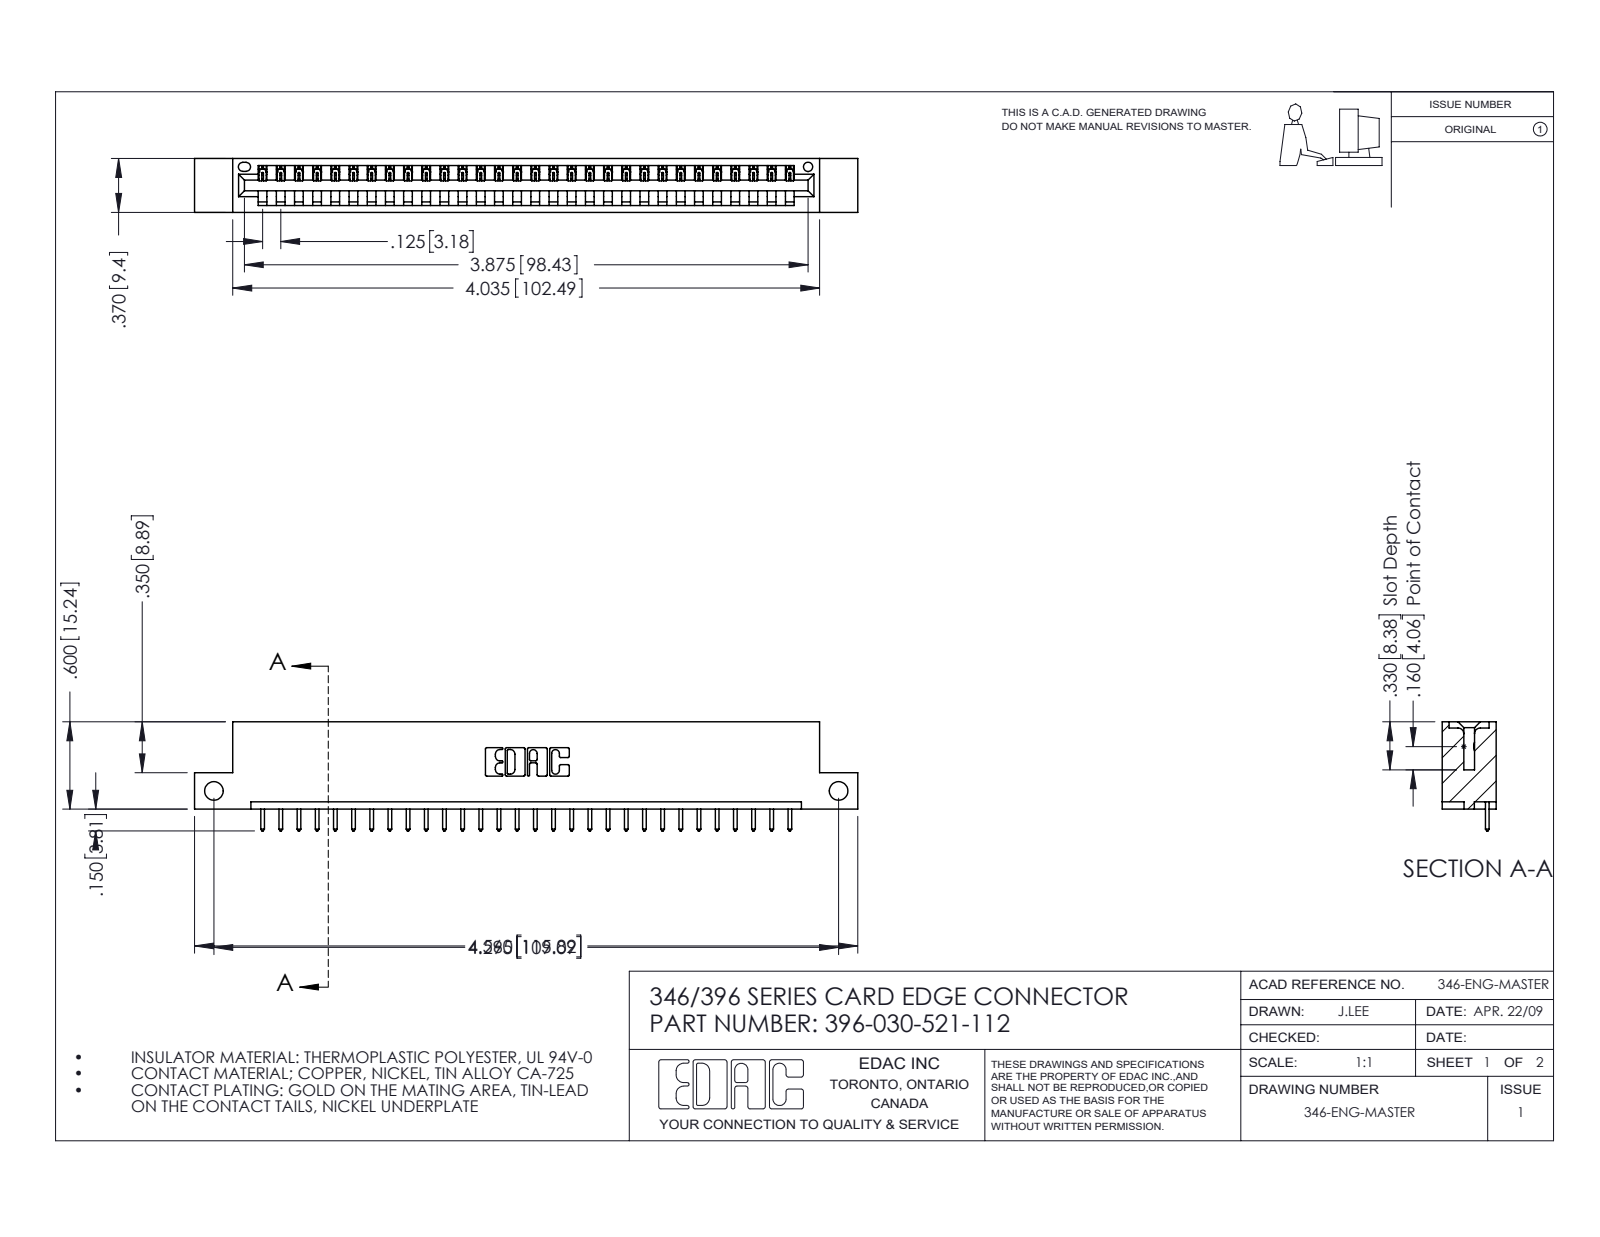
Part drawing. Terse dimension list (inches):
name: 345-292-001_345-293-121; 396-030-521-112; 346 Part_Flush Mounting Lugs - Side Mount
written by: SolidWorks 2016 (CONFIG_CONTROL_DESIGN)
unit: in
bodies: 31 solids, 1862 faces (1276 planar, 586 cylindrical, 0 other)
size: 4.56 × 0.75 × 0.37
volume: 0.661 in³; area: 20.03 in²
holes: 2× ⌀0.128, 1× ⌀0.064
rounds: 60× R0.006, 60× R0.01, 22× R0.01, 6× R0.007, 6× R0.031, 3× R0.026, 2× R0.031, 2× R0.04
face distances: 0.048, 0.322, 0.37, 0.25, 0.072, 0.298, 0.025, 0.148, 0.222, 0.1
hole spacings: 4.295
